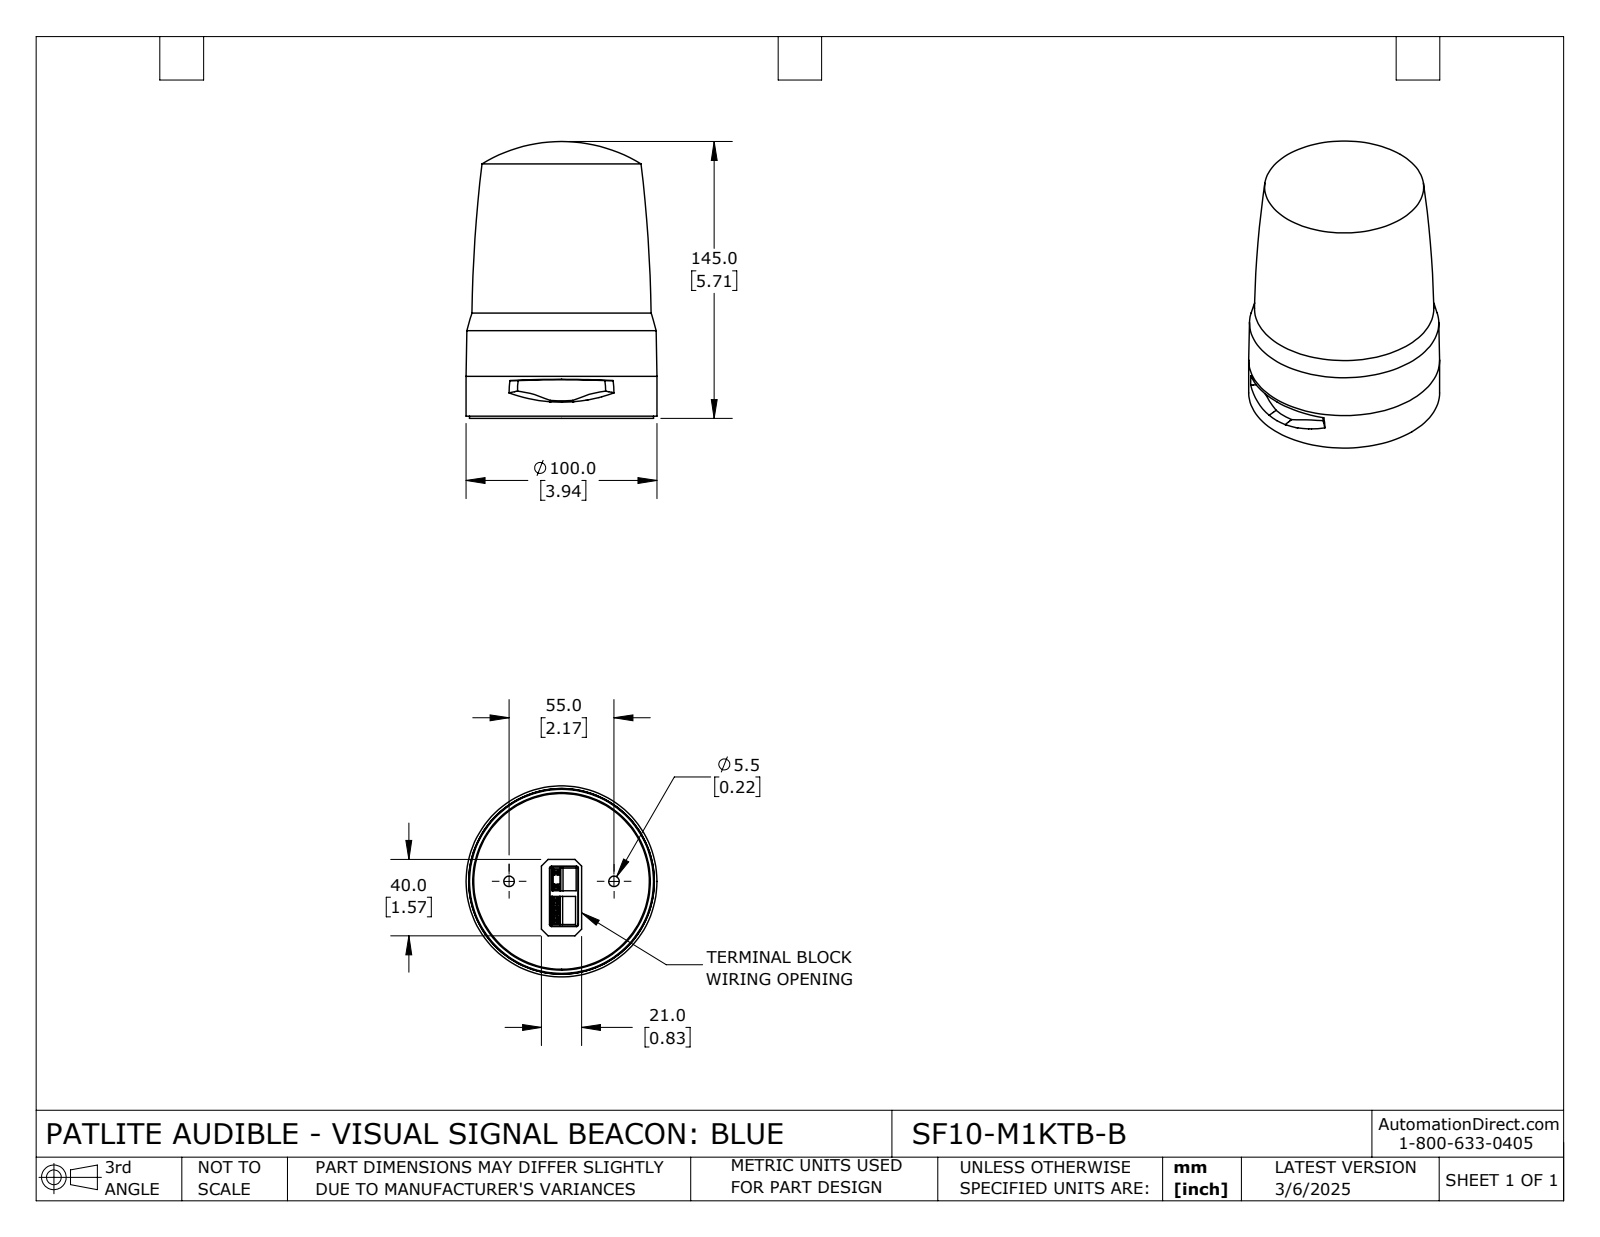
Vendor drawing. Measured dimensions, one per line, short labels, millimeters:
name: SF10-M1KTB-B
written by: SolidWorks 2024 (CONFIG_CONTROL_DESIGN)
unit: mm
bodies: 2 solids, 275 faces (174 planar, 31 cylindrical, 70 other)
size: 145 × 100 × 100
volume: 875 277 mm³; area: 79 857 mm²
holes: 2× ⌀5.5, 2× ⌀13, 1× ⌀93
bosses: 1× ⌀100, 1× ⌀96.4, 1× ⌀94.5, 1× ⌀93.2, 1× ⌀92
rounds: 4× R1, 2× R0.3, 1× R44.75, 1× R45
face distances: 6.3, 18.2, 11.9, 5.6, 12.6, 5.1, 0.4, 4.7, 1.2, 17
hole spacings: 27.5, 55
